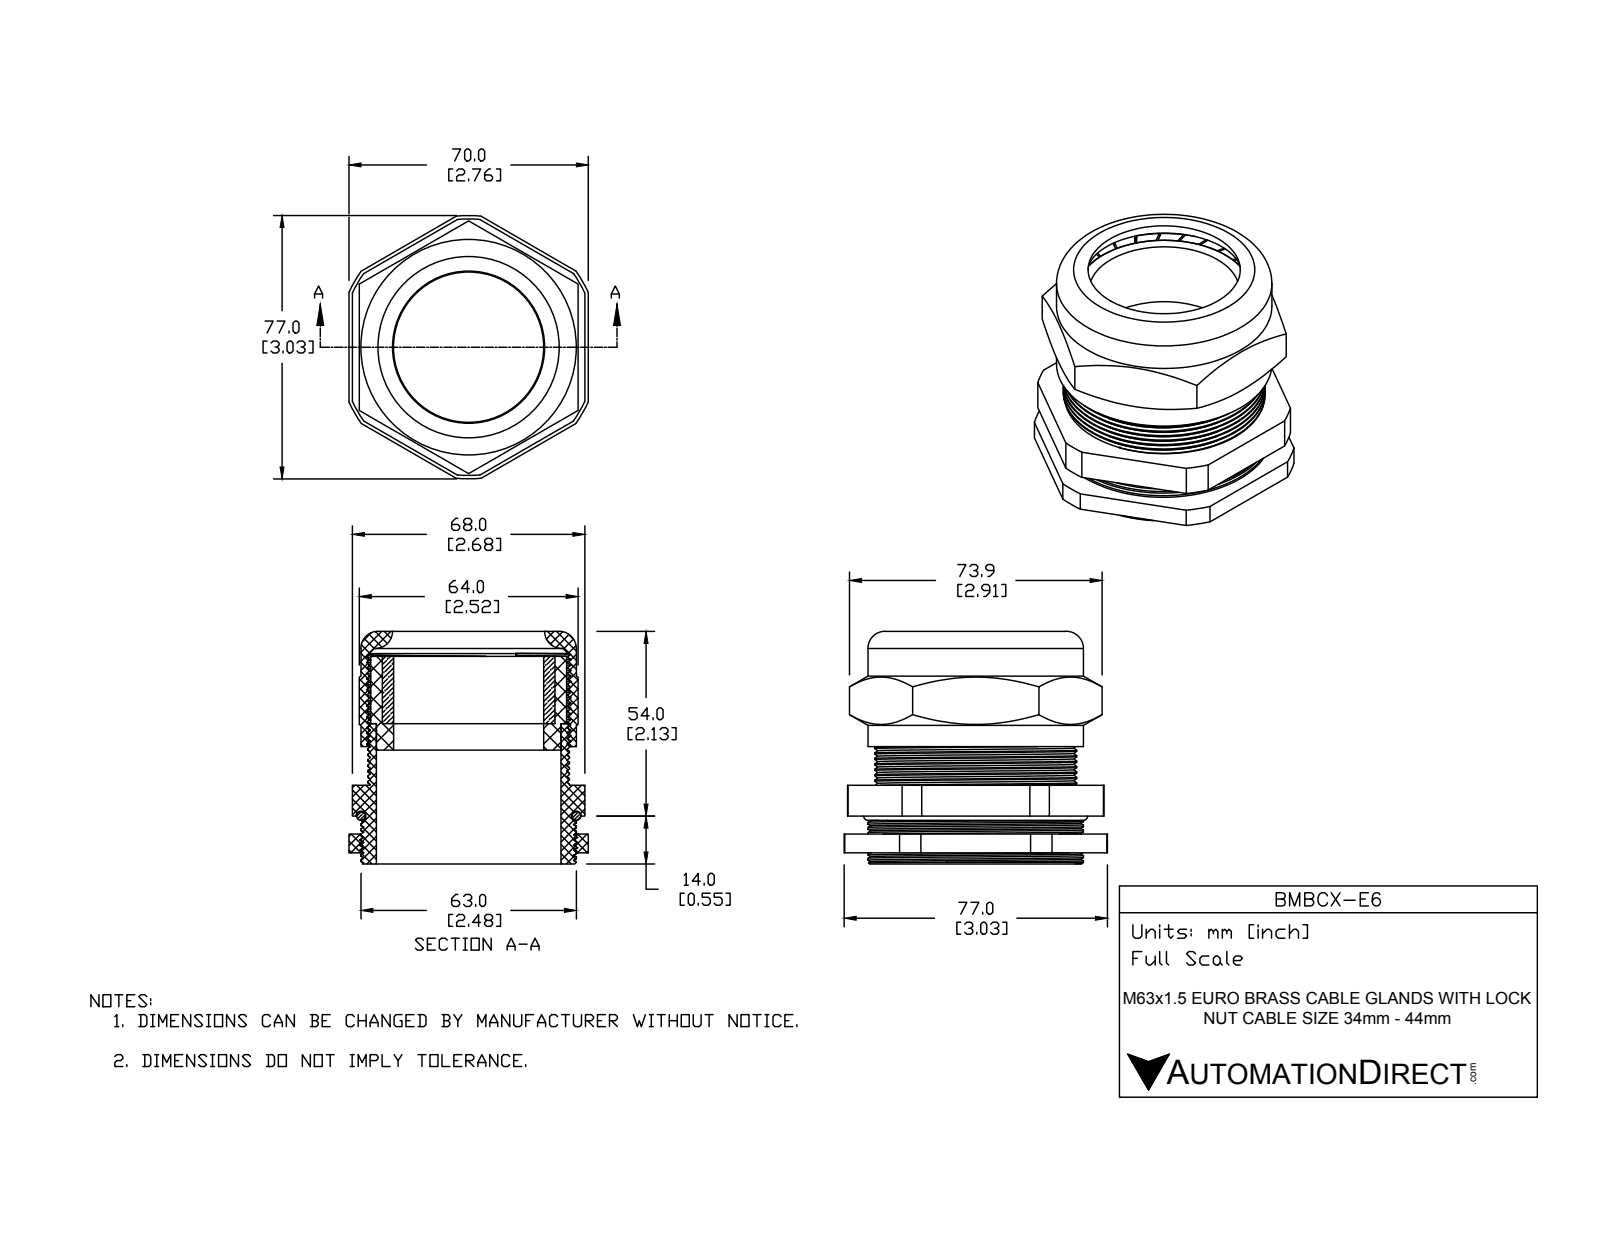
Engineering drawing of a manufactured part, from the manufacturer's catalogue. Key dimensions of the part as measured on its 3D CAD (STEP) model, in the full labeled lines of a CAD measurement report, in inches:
Part name (STEP PRODUCT): BMBCX-E7
STEP written by: SolidWorks 2015 (CONFIG_CONTROL_DESIGN)
Units: inches
Bodies: 6 solids, 284 faces (134 planar, 119 cylindrical, 31 other)
Overall size (bounding box): 3.031 × 2.756 × 2.677
Volume: 5.406 in³ · Surface area: 104.2 in²
Round holes (diameter × count): ⌀1.728 ×1, ⌀1.988 ×1, ⌀2.126 ×1, ⌀2.293 ×1, ⌀2.448 ×1
Round bosses / shafts (diameter × count): ⌀2.48 ×1, ⌀2.323 ×1, ⌀2.256 ×1
Partial cylindrical surfaces — rounded edges, fillets, slot ends (radius × count): R1.476 ×1, R1.516 ×1
Main face-to-face distances: 0.079, 2.598, 2.677, 0.039, 0.02, 0.709, 2.52, 1.063, 0.561, 1.27
